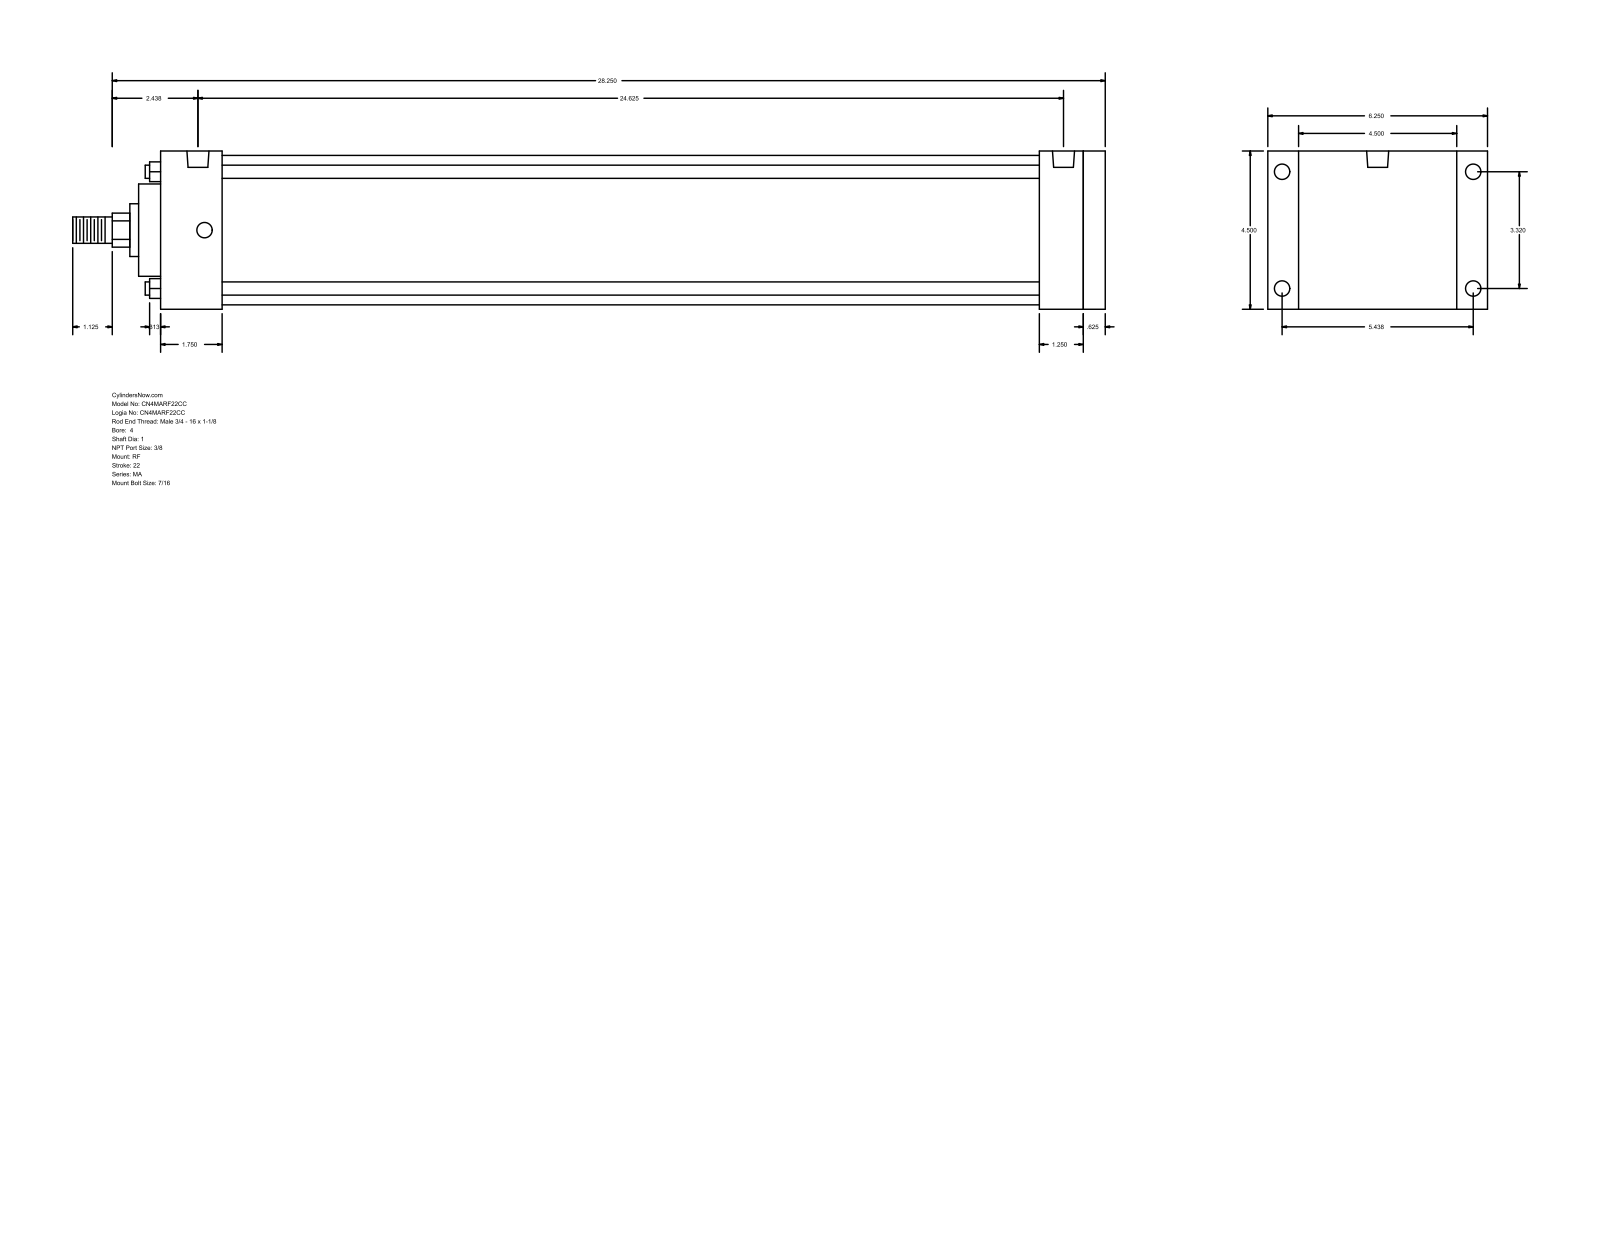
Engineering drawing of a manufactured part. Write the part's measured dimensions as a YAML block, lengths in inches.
part_name: "MA_RF__0400_1"
step_written_by: "GSSL Pune (CONFIG_CONTROL_DESIGN)"
units: inches
bodies: {solids: 0, faces: 94, planar: 65, cylindrical: 29, other: 0}
overall_size: [29.375, 6.25, 4.5]
round_holes:
  - {diameter: 0.437, count: 8}
  - {diameter: 0.627, count: 2}
round_bosses_or_shafts:
  - {diameter: 0.375, count: 4}
  - {diameter: 4.25, count: 1}
  - {diameter: 2.625, count: 1}
  - {diameter: 1.5, count: 1}
  - {diameter: 1, count: 1}
  - {diameter: 0.75, count: 1}
partial_cylinders:
  - {radius: 0.484, count: 1}
face_to_face_distances: [4.5, 26.875, 26.25, 0.625, 0.875, 5.375, 25, 1.25, 1.875, 1.75]
hole_center_spacings: [3.32, 5.438, 6.371, 24.25, 0.187, 0.188, 24.437, 24.438]
